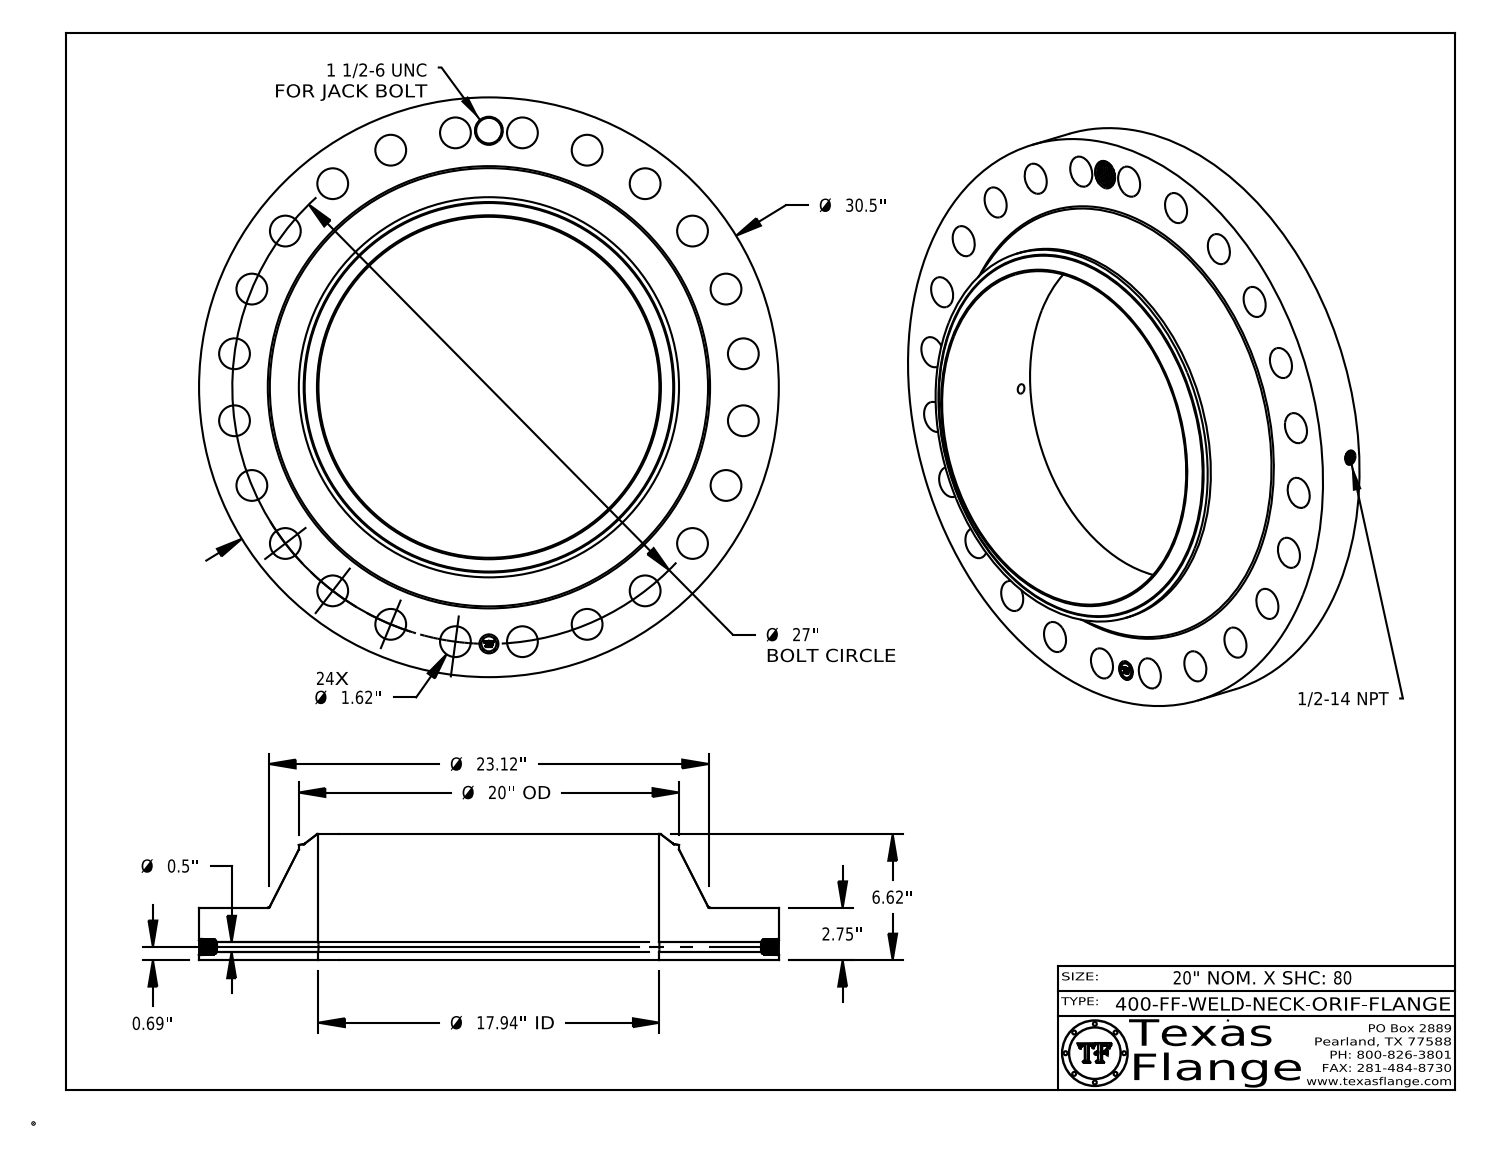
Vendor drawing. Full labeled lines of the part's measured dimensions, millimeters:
Part name (STEP PRODUCT): 400-FF-WELD-NECK
STEP written by: CATIA V5 STEP AP214 (AUTOMOTIVE_DESIGN)
Units: millimetres
Bodies: 1 solid, 811 faces (368 planar, 127 cylindrical, 316 other)
Overall size (bounding box): 774.7 × 774.7 × 168.1
Volume: 25 350 000 mm³ · Surface area: 1 302 000 mm²
Round holes (diameter × count): ⌀41.1 ×24, ⌀12.7 ×1, ⌀17.1 ×1, ⌀25.4 ×1, ⌀34.1 ×1, ⌀455.6 ×1
Round bosses / shafts (diameter × count): ⌀1.5 ×8, ⌀774.7 ×1, ⌀508 ×1, ⌀20 ×1
Main face-to-face distances: 69.9, 168.1, 98.3, 69.5, 0.4, 98.7, 7.6, 7.4, 1.4, 6.3
Hole centre spacings: 342.9, 593.9, 633.6, 544.1, 89.5, 177.5, 484.9, 662.4
